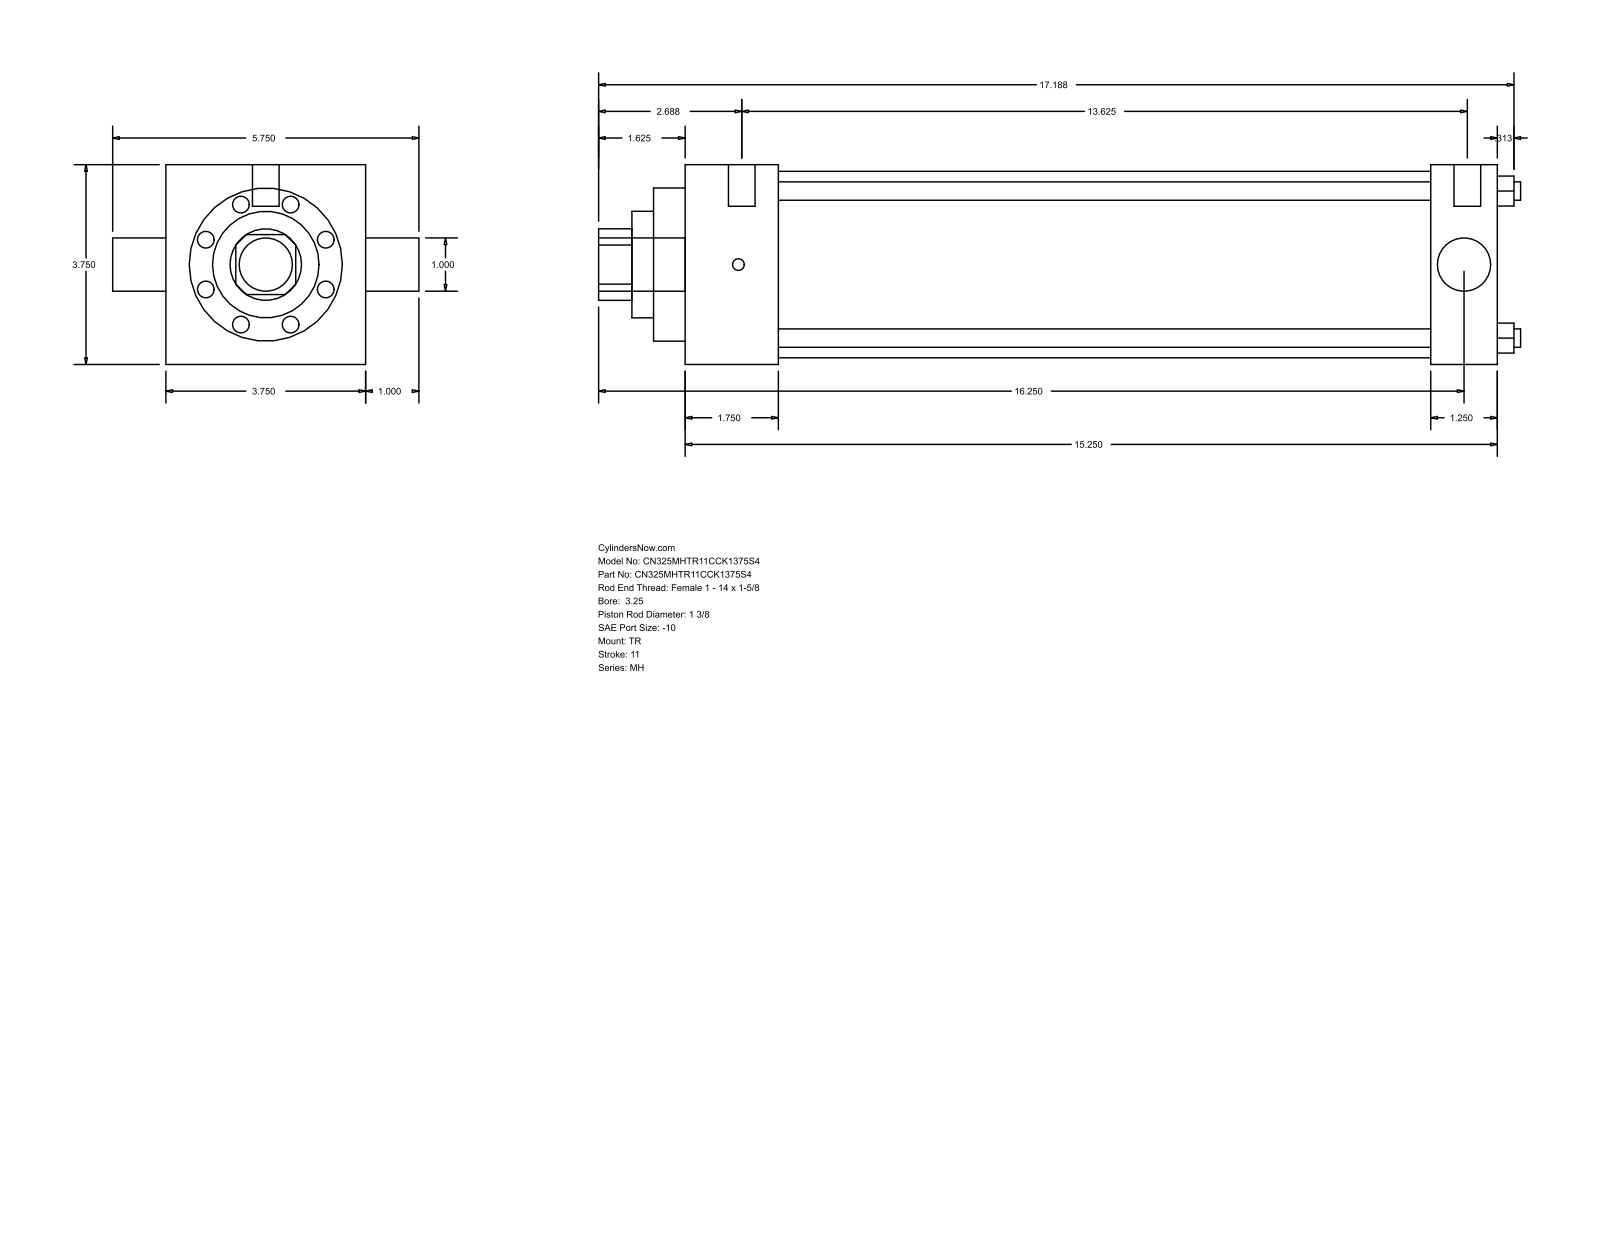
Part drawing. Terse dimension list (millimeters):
name: MH_TR__0325_1.375
written by: GSSL Pune (CONFIG_CONTROL_DESIGN)
unit: mm
bodies: 0 solids, 86 faces (61 planar, 25 cylindrical, 0 other)
size: 439.74 × 146.05 × 95.25
holes: 4× ⌀8.76, 1× ⌀25.4, 1× ⌀34.92, 1× ⌀50.8, 1× ⌀73.03, 1× ⌀88.9
bosses: 3× ⌀5.56, 2× ⌀12.7, 1× ⌀25.4
rounds: 1× R17.06
face distances: 95.24, 387.35, 44.45, 355.61, 311.16, 342.9, 31.74, 15.08, 59.53, 370.69
hole spacings: 49.57, 70.1, 99.14
